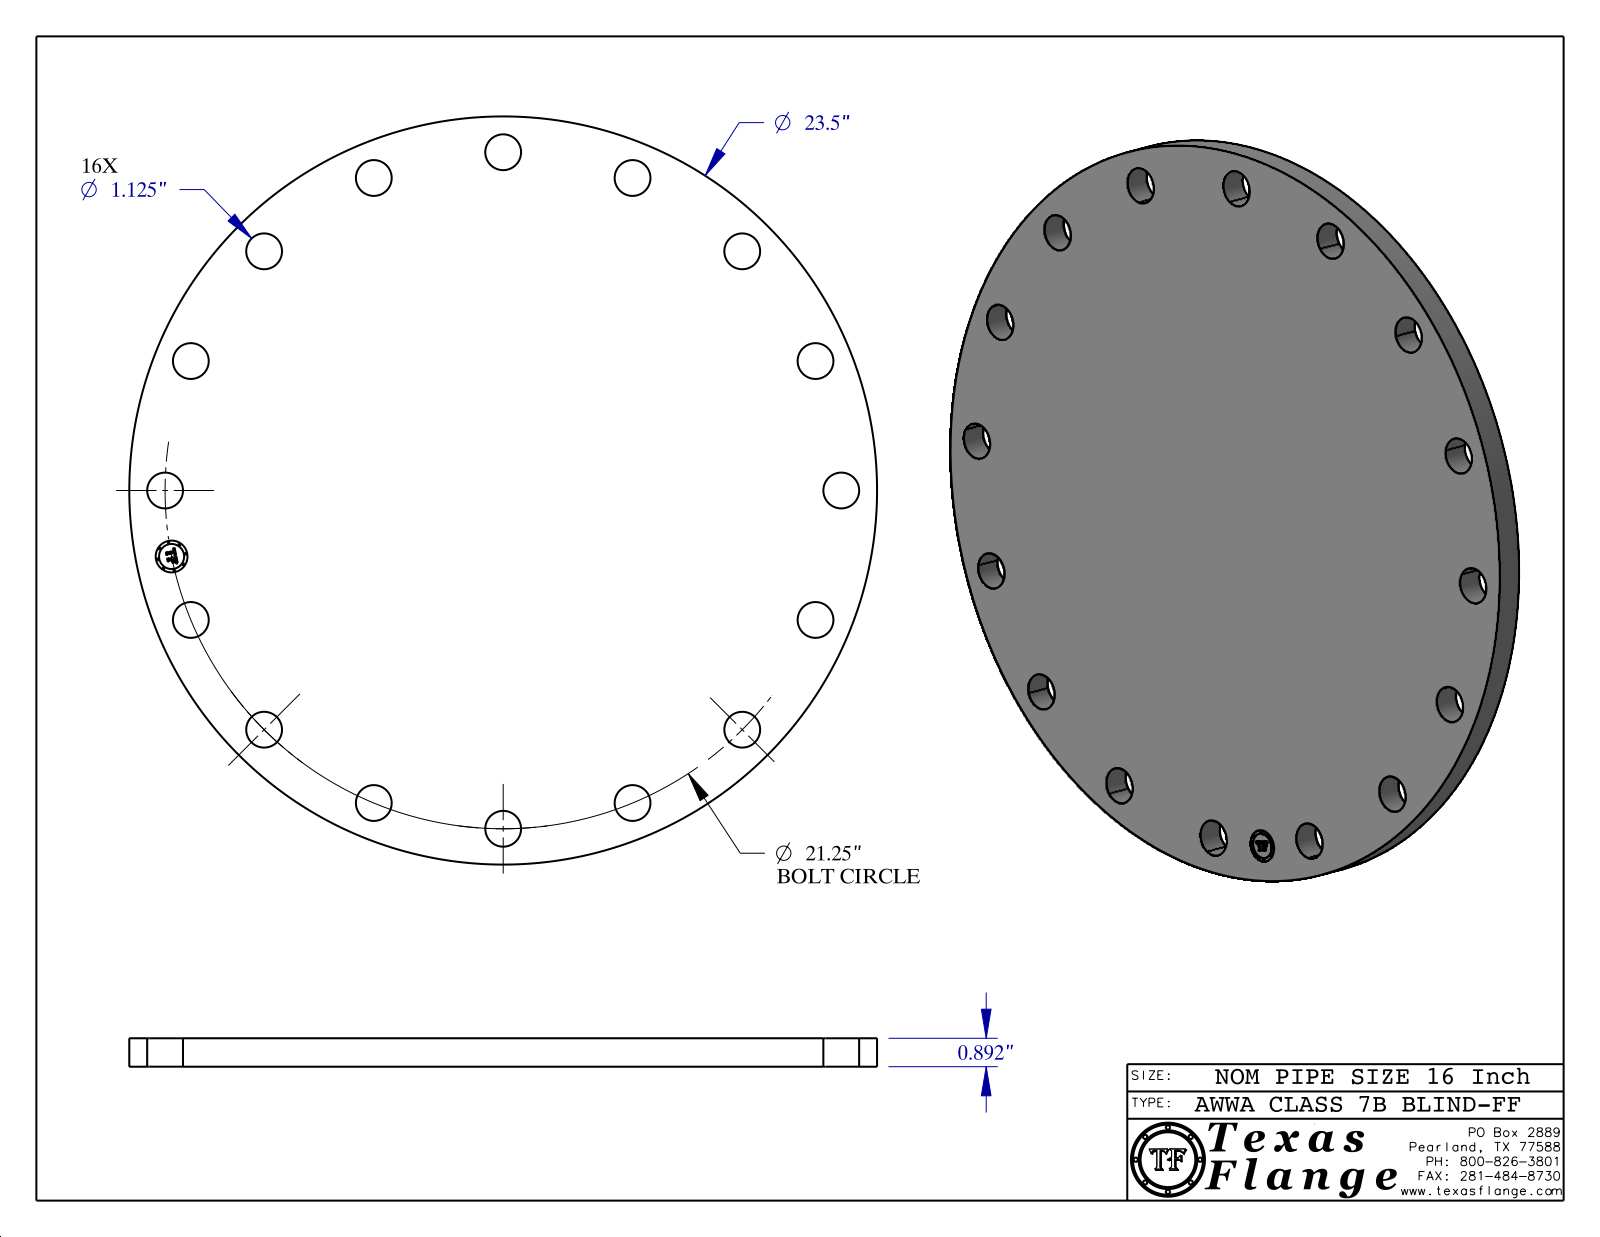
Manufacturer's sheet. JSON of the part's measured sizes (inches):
{"part_name": "AWWA Class 7B-BLIND-FF", "step_written_by": "CATIA V5 STEP AP214 (AUTOMOTIVE_DESIGN)", "units": "inches", "bodies": {"solids": 1, "faces": 421, "planar": 367, "cylindrical": 54, "other": 0}, "overall_size": [23.5, 23.5, 0.892], "volume_in3": 372.7, "surface_area_in2": 952.1, "round_holes": [[1.125, 16], [1, 1]], "round_bosses_or_shafts": [[0.061, 8], [23.5, 1], [0.788, 1]], "face_to_face_distances": [0.892, 0.015, 0.877, 0.298, 0.292, 0.055, 0.193, 0.248, 0.044, 0.15], "hole_center_spacings": [4.146, 11.806, 20.842, 8.132, 15.026, 19.633, 17.669, 17.669]}
